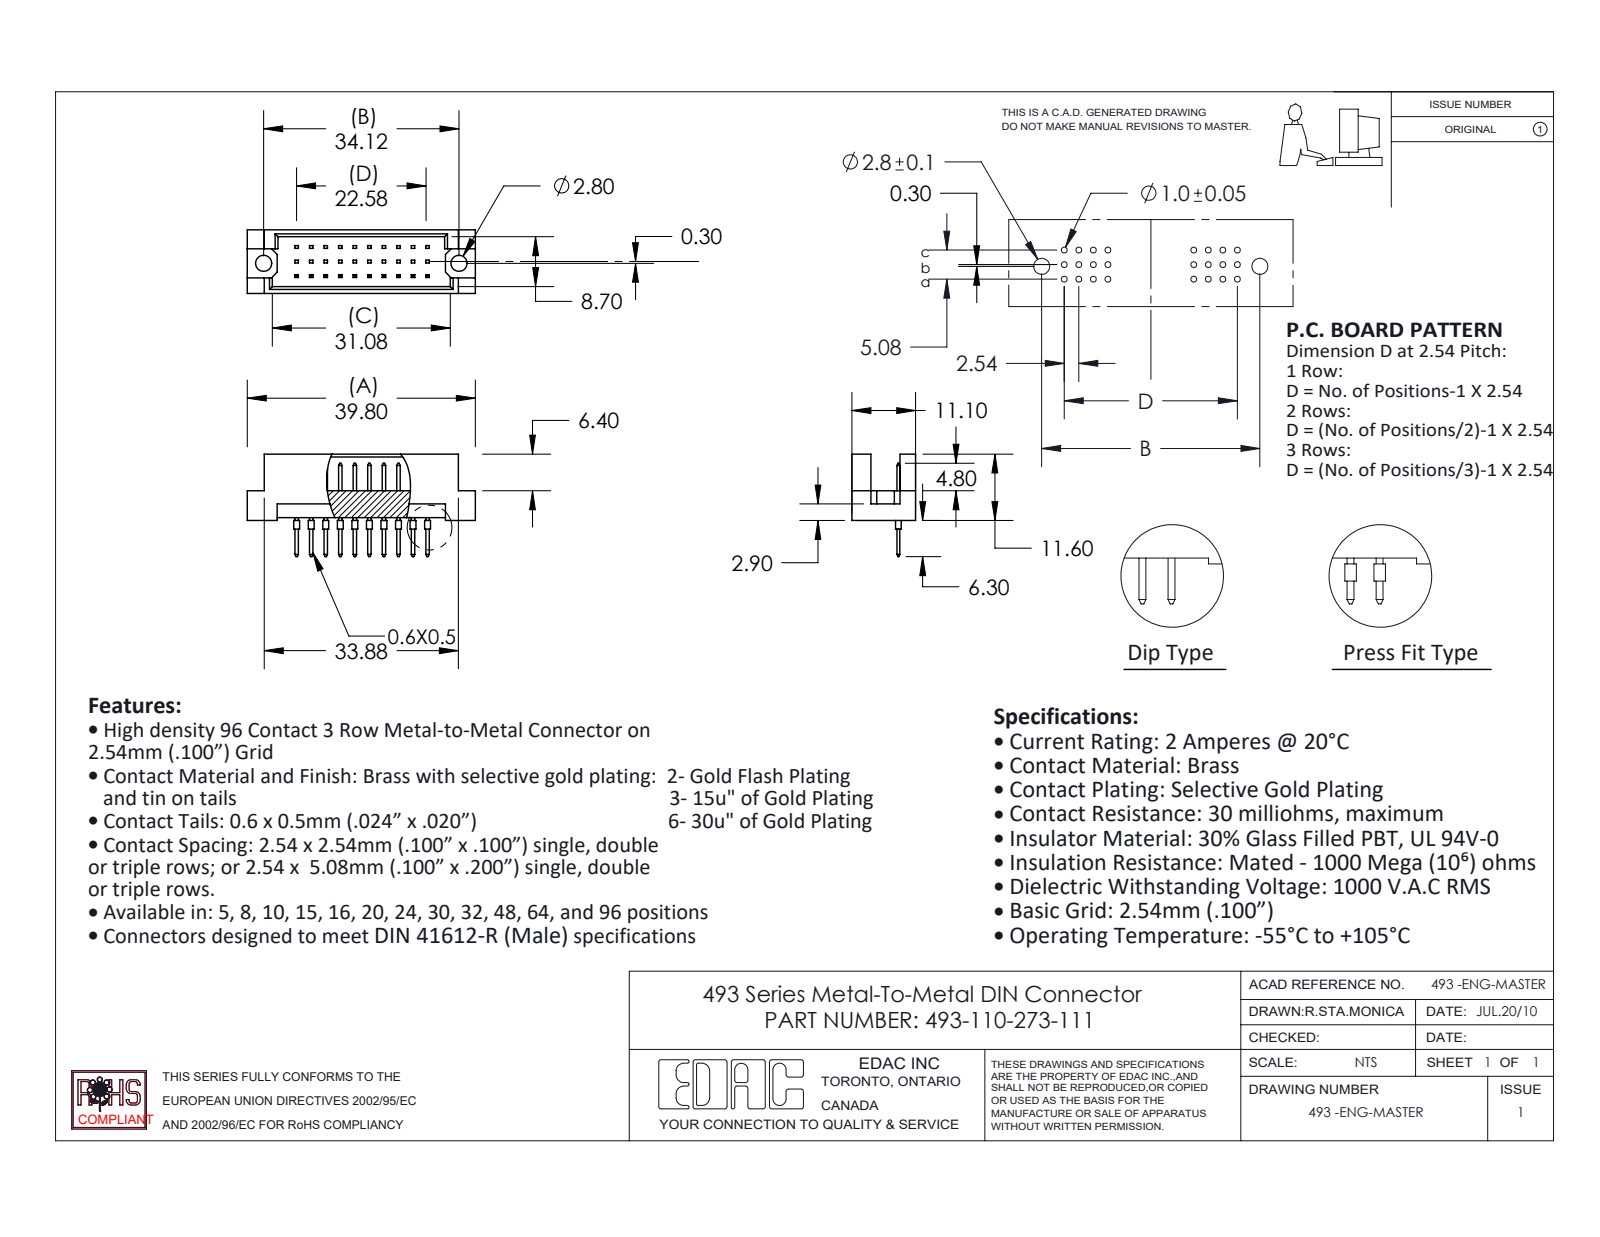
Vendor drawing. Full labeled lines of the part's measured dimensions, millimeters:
Part name (STEP PRODUCT): 493 Part_30; 493-290_73; 493-110-273-111
STEP written by: SolidWorks 2020 (CONFIG_CONTROL_DESIGN)
Units: millimetres
Bodies: 11 solids, 392 faces (368 planar, 24 cylindrical, 0 other)
Overall size (bounding box): 39.8 × 17.9 × 11.1
Volume: 2 428 mm³ · Surface area: 3 116 mm²
Round holes (diameter × count): ⌀2.8 ×2
Round bosses / shafts (diameter × count): ⌀1 ×10
Main face-to-face distances: 1.2, 9.9, 11.1, 8.7, 2.54, 0.5, 4.7, 5.08, 2.76, 3.26
Hole centre spacings: 34.12
